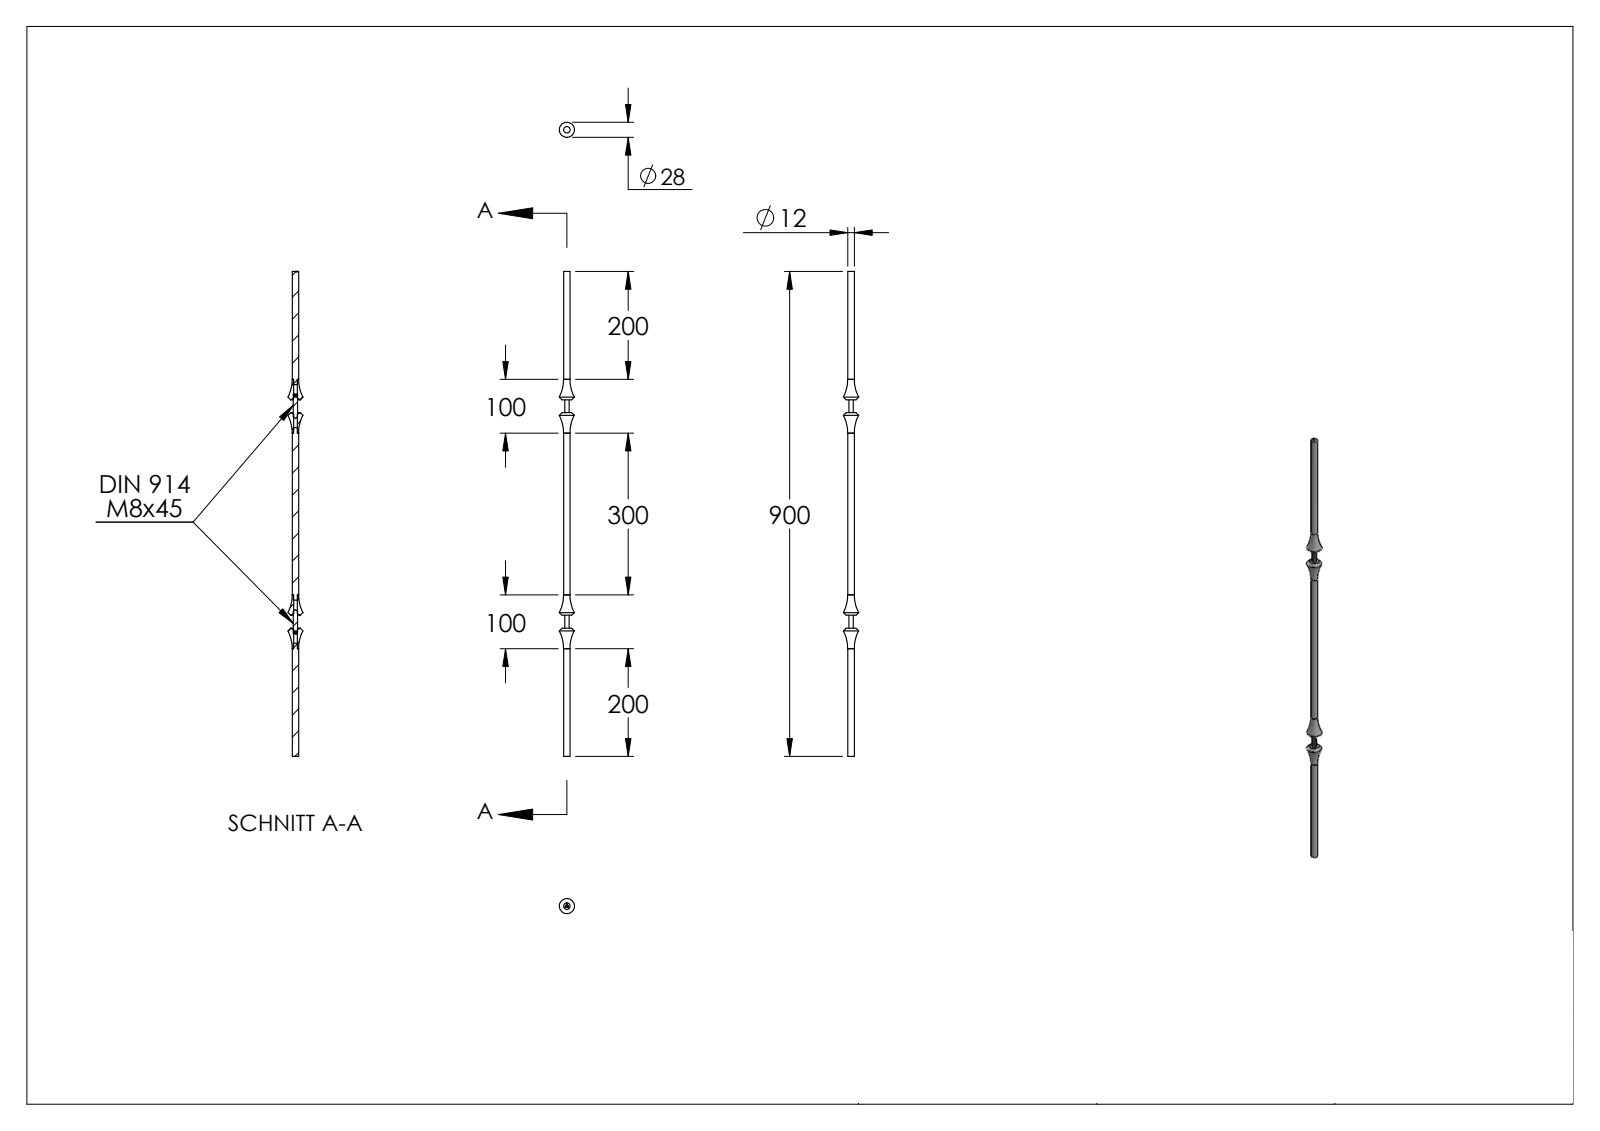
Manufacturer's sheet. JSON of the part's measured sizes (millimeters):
{"part_name": "56105-240D; DIN914_DIN 914 M8x45; 56105-240D Teil3_56105-240D Teil3; 56105-240D Teil1_56105-240 Teil1 (+5 more)", "step_written_by": "SolidWorks 2018 (CONFIG_CONTROL_DESIGN)", "units": "millimeters", "bodies": {"solids": 9, "faces": 383, "planar": 193, "cylindrical": 26, "other": 164}, "overall_size": [70000, 8000, 8000], "volume_mm3": 120143, "surface_area_mm2": 44294, "round_holes": [[6.8, 1]], "round_bosses_or_shafts": [[12, 1], [8, 1]], "face_to_face_distances": [300, 400, 100, 200, 600, 700, 500, 10, 90, 900]}
